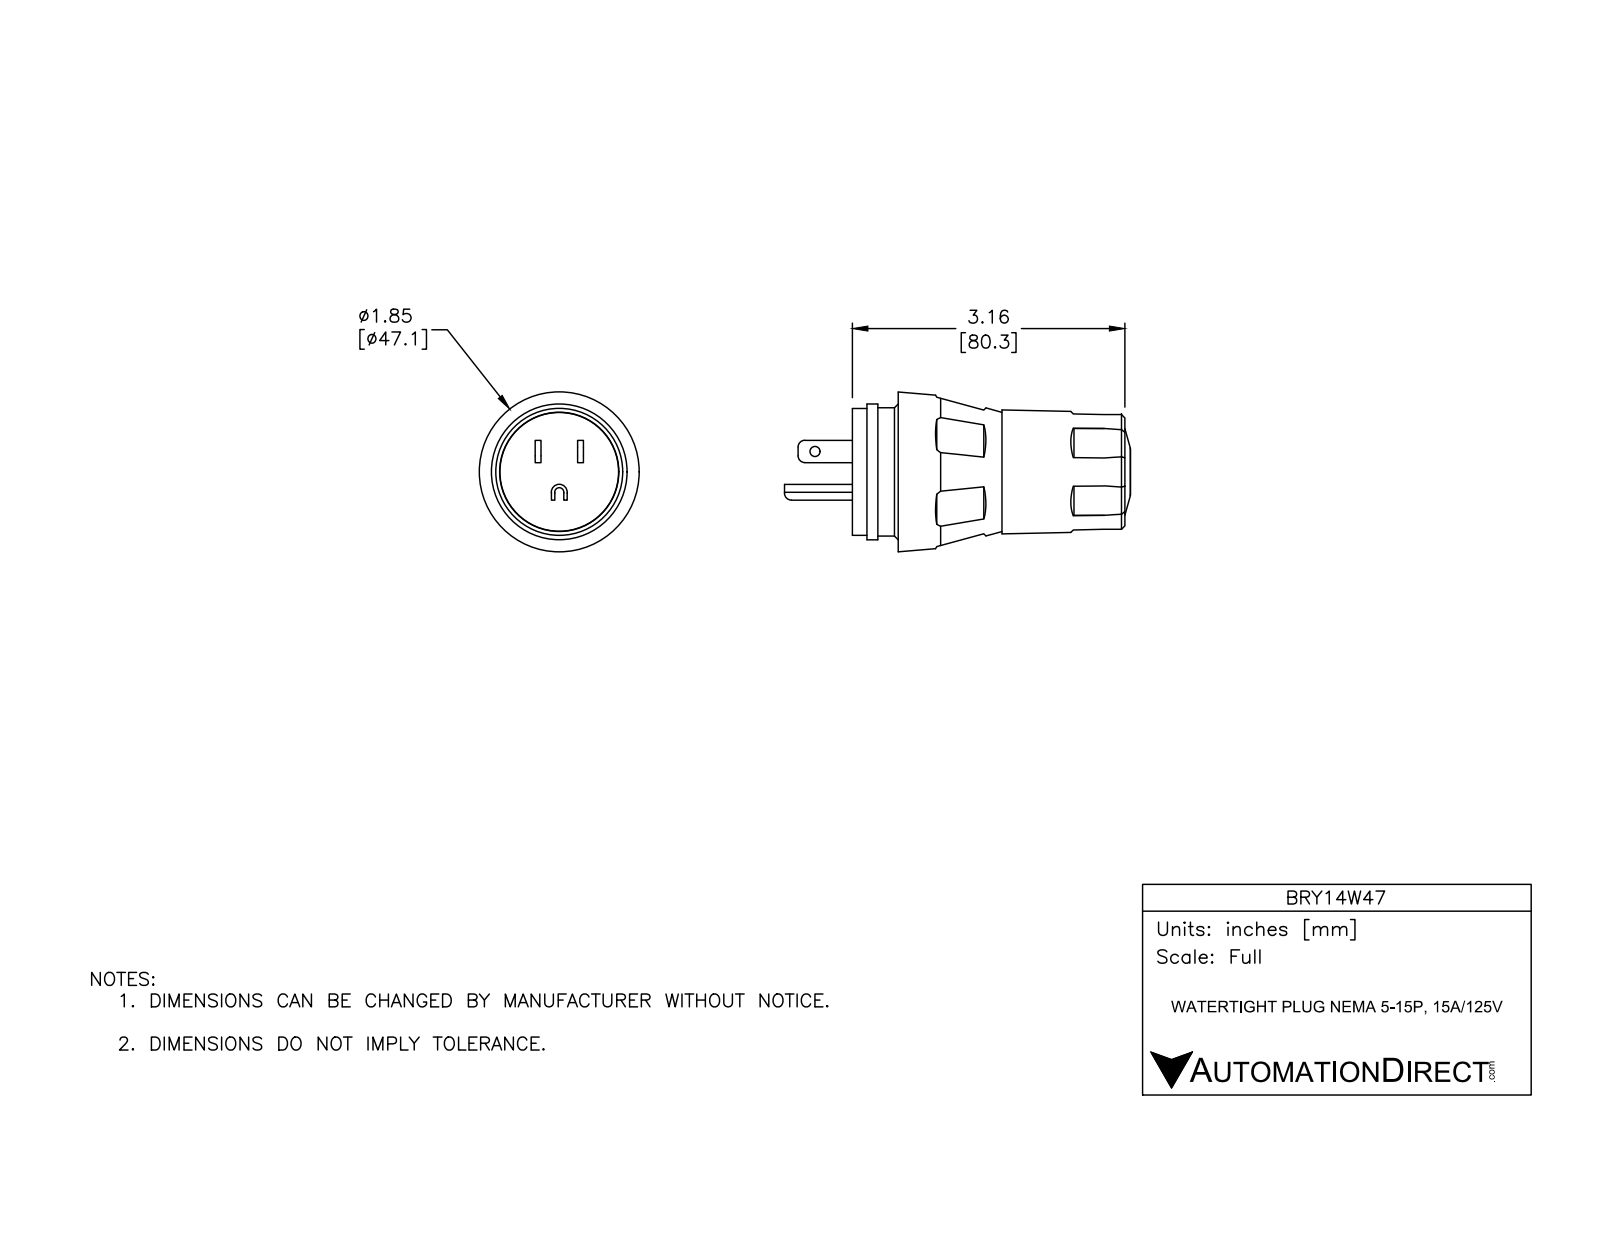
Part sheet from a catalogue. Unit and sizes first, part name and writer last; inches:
Units: inches
Overall size (bounding box): 4.015 × 1.854 × 1.854
Round holes (diameter × count): ⌀0.118 ×1, ⌀0.453 ×1, ⌀1.004 ×1, ⌀1.382 ×1
Round bosses / shafts (diameter × count): ⌀1.575 ×1, ⌀1.488 ×1, ⌀1.472 ×1, ⌀1.378 ×1, ⌀0.993 ×1
Partial cylindrical surfaces — rounded edges, fillets, slot ends (radius × count): R0.079 ×3, R0.052 ×1, R0.092 ×1
Main face-to-face distances: 0.276, 2.291, 2.567, 2.035, 0.256, 0.531, 1.331, 0.516, 2.551, 2.807
Volume: 5.433 in³ · Surface area: 36.61 in²
Bodies: 7 solids, 133 faces (80 planar, 30 cylindrical, 23 other)
Part name (STEP PRODUCT): BRY14W47
STEP written by: SolidWorks 2016 (AUTOMOTIVE_DESIGN)
